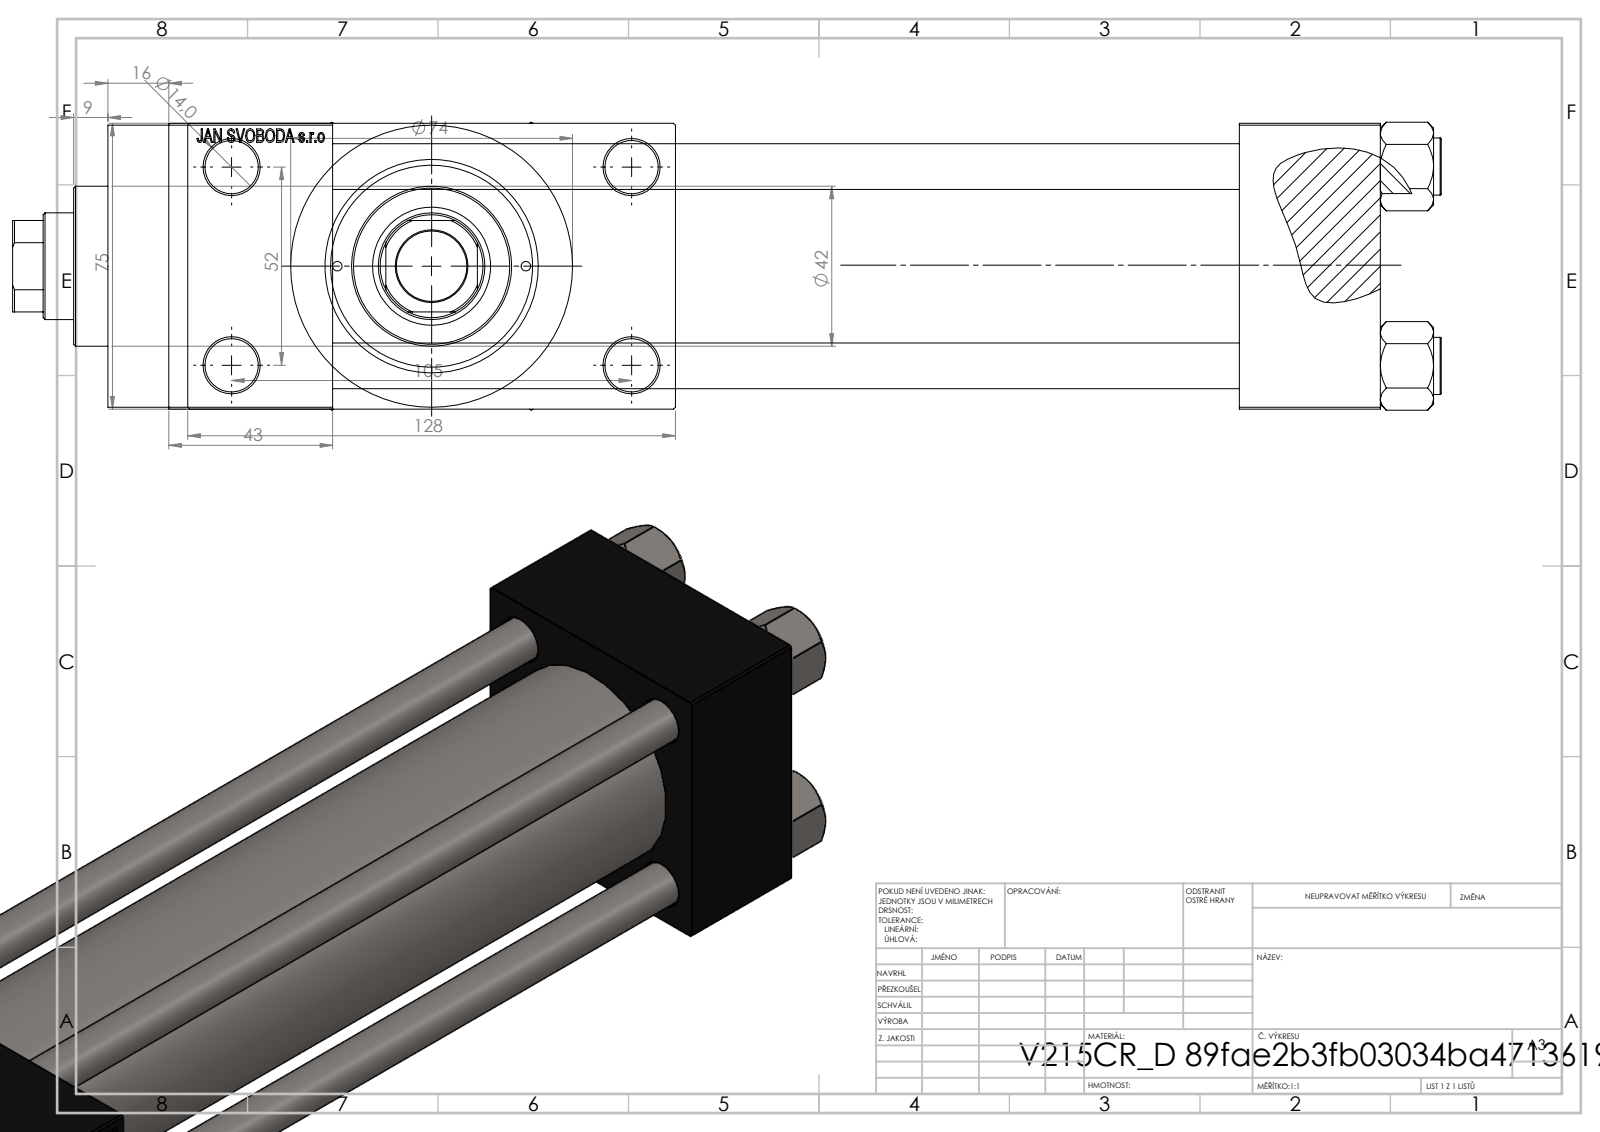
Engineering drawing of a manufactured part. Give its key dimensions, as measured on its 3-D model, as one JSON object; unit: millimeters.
{"part_name": "V215_VC_A; NUT_M5_D; V215CR_D_Body; V215CR_VCP_D (+1 more)", "step_written_by": "SolidWorks 2019 (CONFIG_CONTROL_DESIGN)", "units": "millimeters", "bodies": {"solids": 11, "faces": 1111, "planar": 499, "cylindrical": 92, "other": 520}, "overall_size": [375, 128, 75.54], "volume_mm3": 1088000, "surface_area_mm2": 273462, "round_holes": [[12, 4], [14, 4], [2.5, 2], [7, 2], [20.96, 2], [30, 2], [18.5, 1], [28, 1], [31, 1], [41, 1], [50, 1], [53, 1]], "round_bosses_or_shafts": [[15, 4], [74, 1], [56, 1], [42, 1]], "partial_cylinders_radius": [[13.5, 1]], "face_to_face_distances": [75, 238, 37, 275, 26.5, 318, 281, 43, 101.5, 16], "hole_center_spacings": [26.19, 26.35, 36.98, 38.03, 52.3, 57.22, 58.43, 58.59]}
